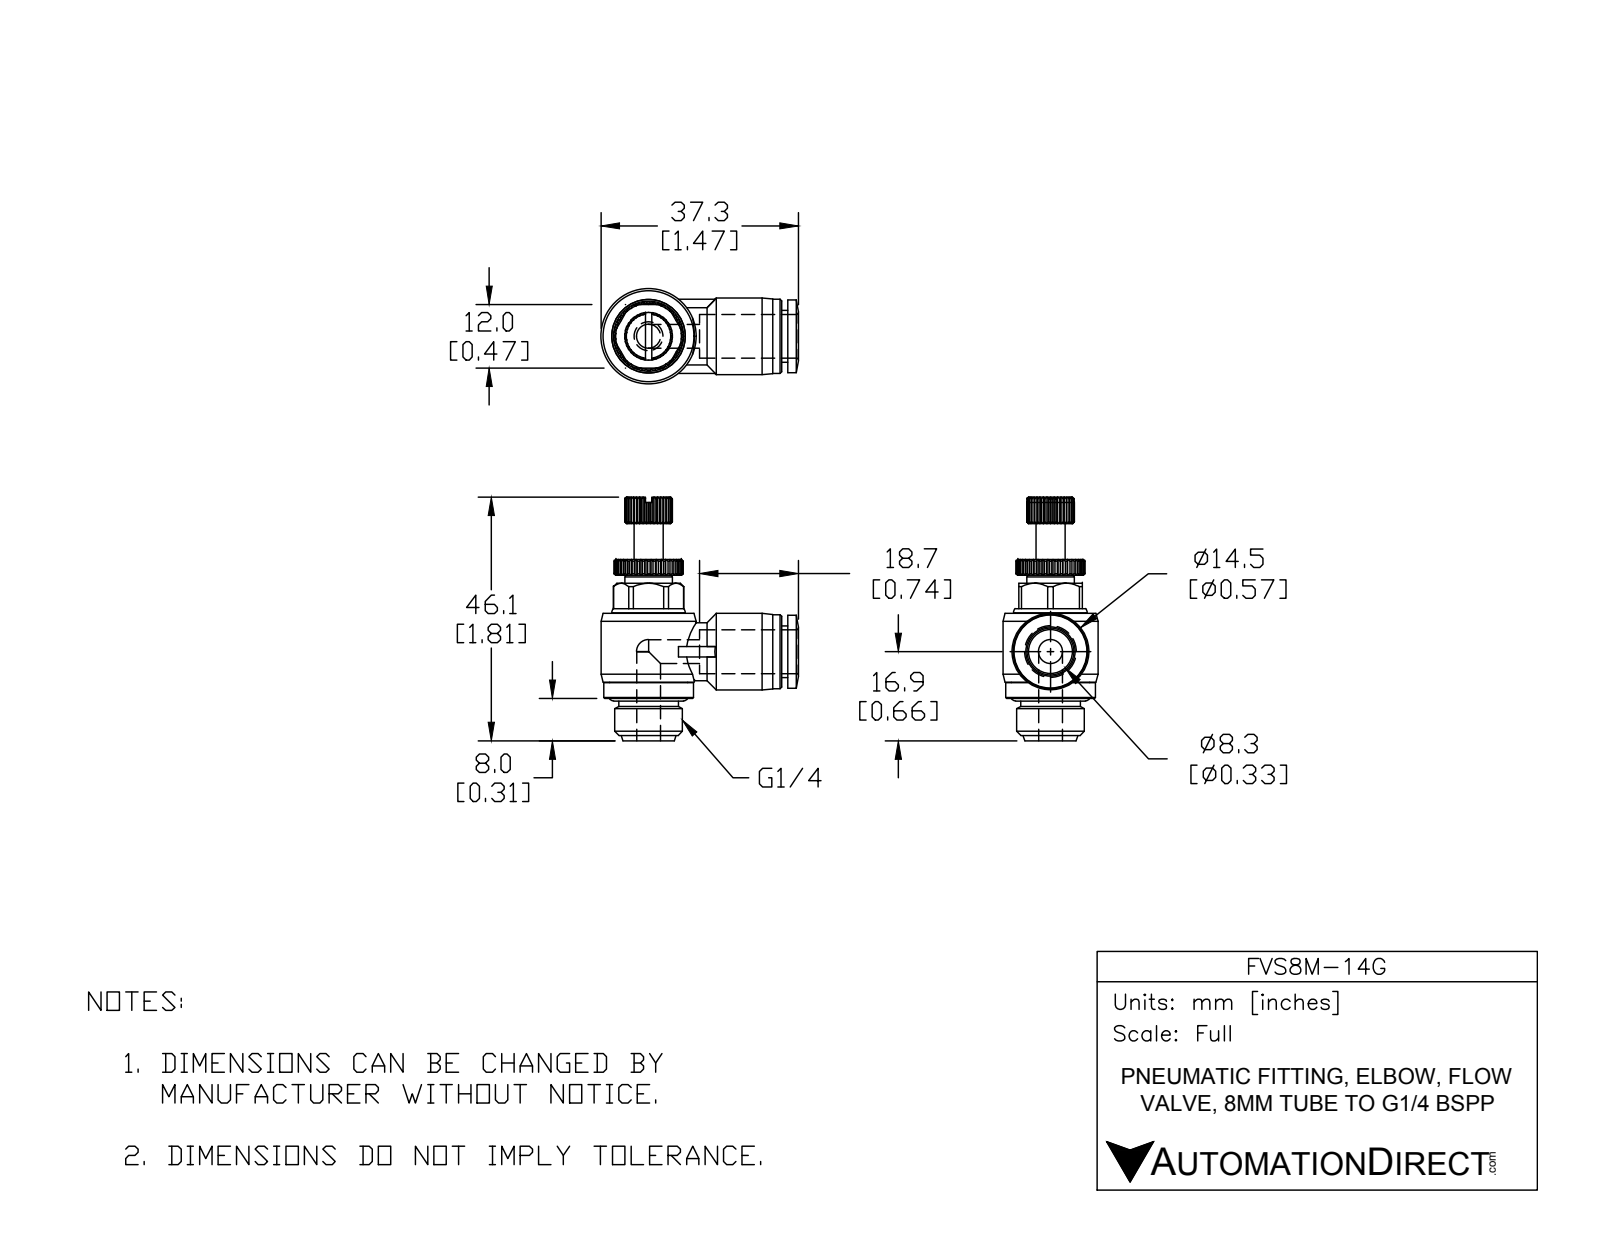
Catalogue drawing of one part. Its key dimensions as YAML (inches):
part_name: "FVS8M-14G"
step_written_by: "SolidWorks 2015 (AUTOMOTIVE_DESIGN)"
units: inches
bodies: {solids: 2, faces: 515, planar: 196, cylindrical: 119, other: 200}
overall_size: [1.815, 1.47, 0.709]
volume: 0.489
surface_area: 7.705
round_holes:
  - {diameter: 0.177, count: 2}
  - {diameter: 0.327, count: 1}
round_bosses_or_shafts:
  - {diameter: 0.709, count: 1}
  - {diameter: 0.669, count: 1}
  - {diameter: 0.583, count: 1}
  - {diameter: 0.571, count: 1}
  - {diameter: 0.551, count: 1}
  - {diameter: 0.543, count: 1}
  - {diameter: 0.528, count: 1}
  - {diameter: 0.504, count: 1}
partial_cylinders:
  - {radius: 0.256, count: 1}
  - {radius: 0.262, count: 1}
face_to_face_distances: [0.402, 0.512, 0.118, 0.472, 0.234, 0.917, 0.913, 0.516, 0.045, 0.283]
